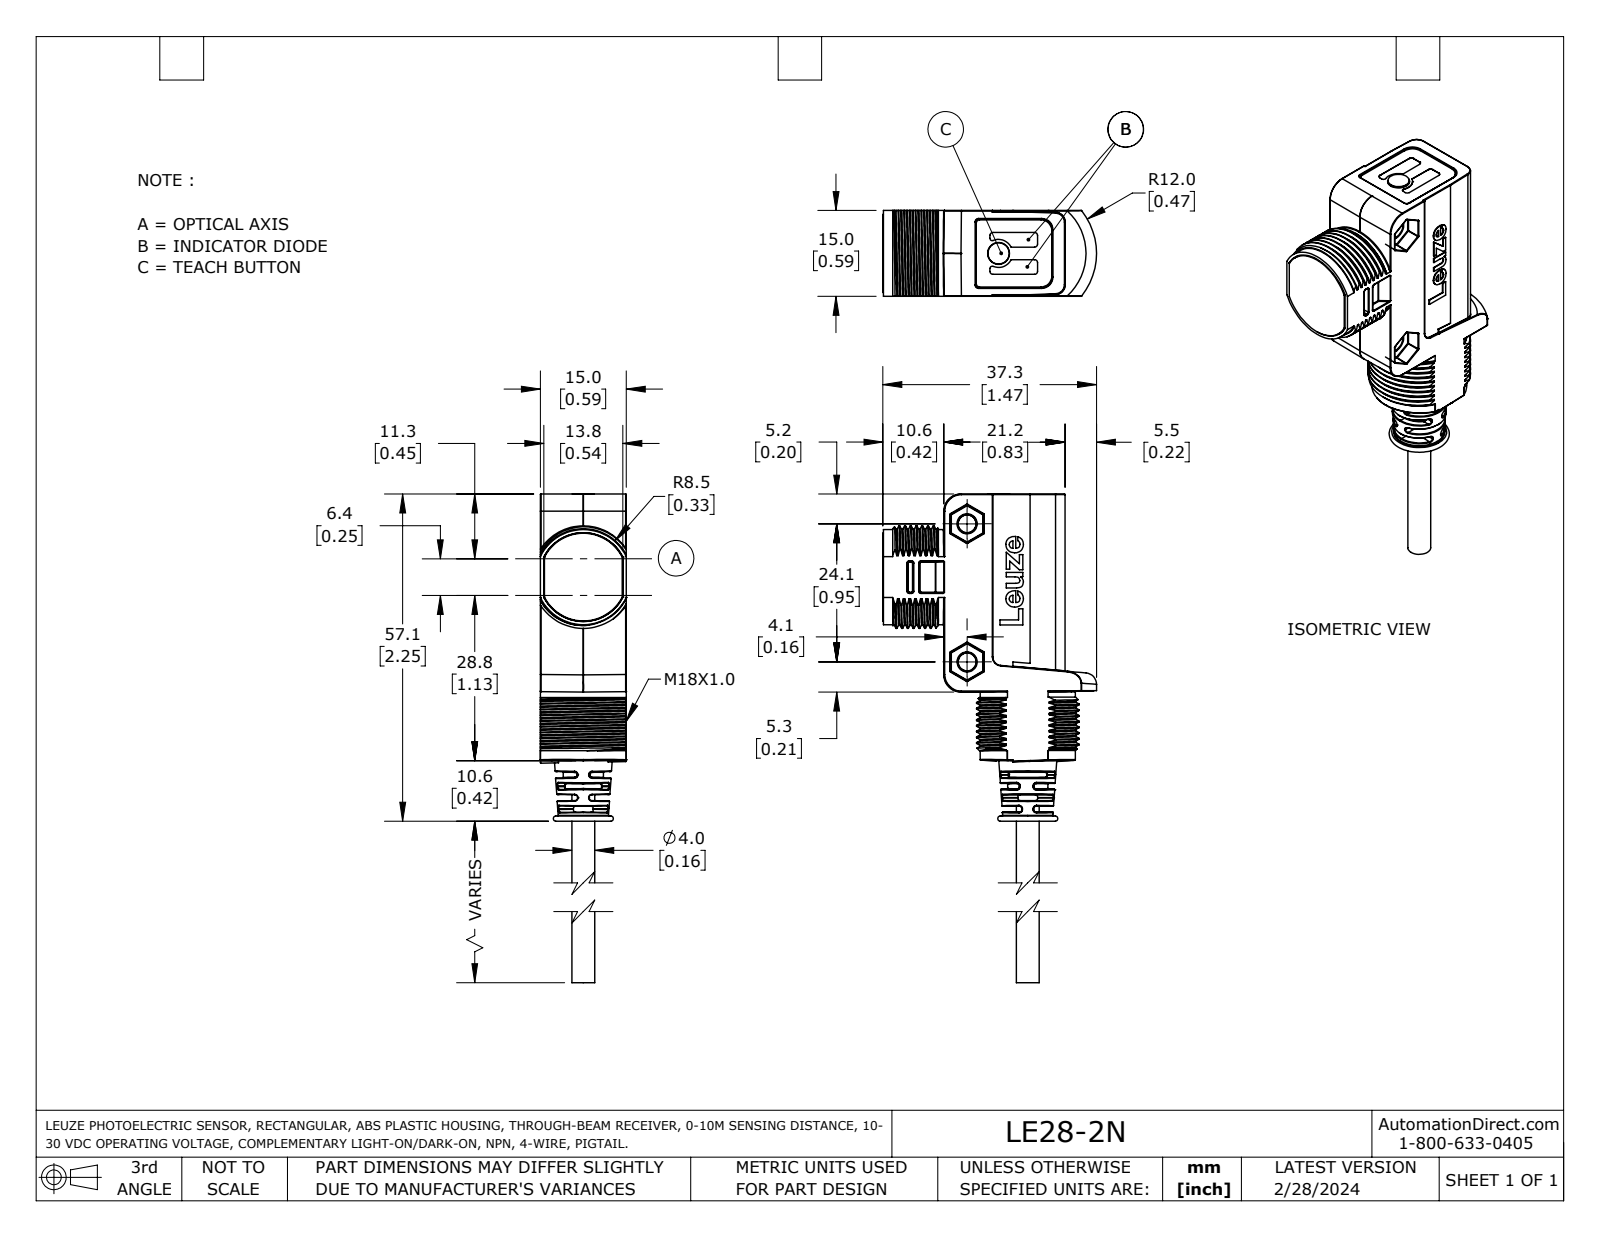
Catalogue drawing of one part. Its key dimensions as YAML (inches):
part_name: "3d_br28_kab"
step_written_by: "SolidWorks 2023 (AUTOMOTIVE_DESIGN)"
units: inches
bodies: {solids: 1, faces: 938, planar: 253, cylindrical: 309, other: 376}
overall_size: [3.189, 1.469, 0.591]
volume: 1.002
surface_area: 9.538
round_bosses_or_shafts:
  - {diameter: 0.276, count: 1}
  - {diameter: 0.157, count: 1}
partial_cylinders:
  - {radius: 0.004, count: 134}
  - {radius: 0.02, count: 29}
  - {radius: 0.075, count: 4}
  - {radius: 0.118, count: 4}
  - {radius: 0.016, count: 2}
  - {radius: 0.024, count: 2}
  - {radius: 0.067, count: 2}
  - {radius: 0.122, count: 2}
face_to_face_distances: [0.591, 0.583, 0.575, 1.252, 1.248, 0.039, 0.157, 0.098, 0.492, 0.484]
